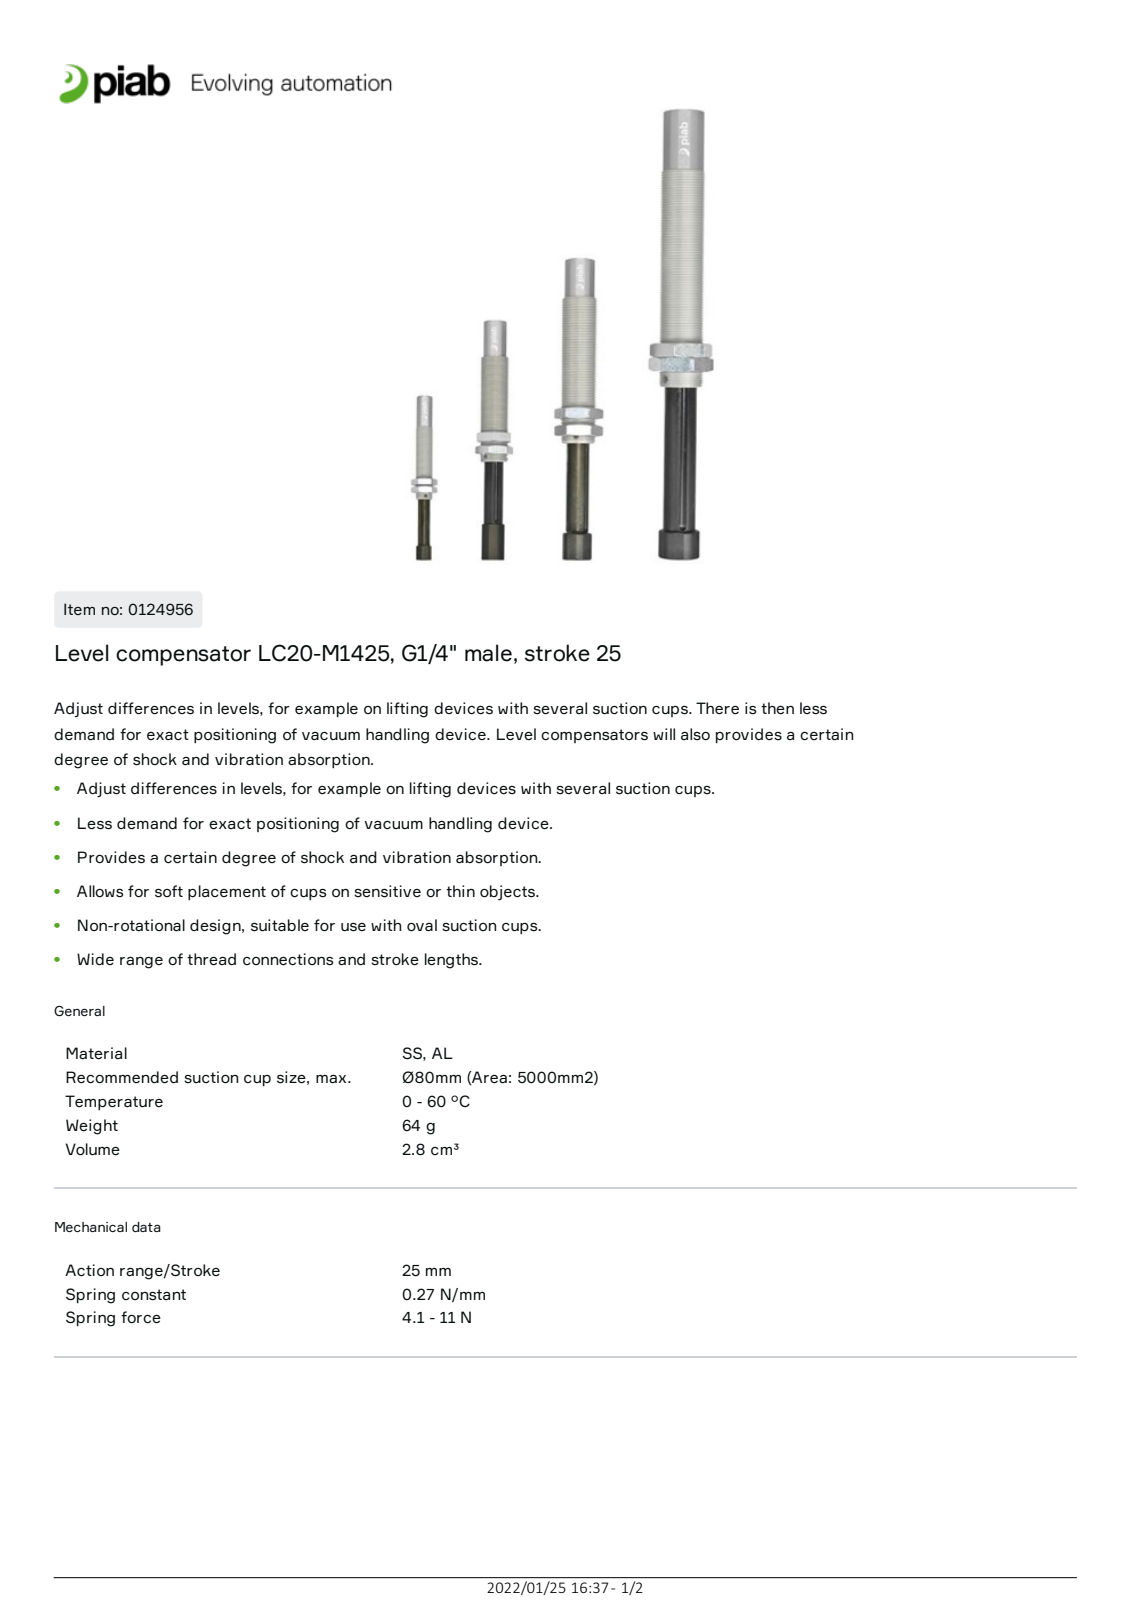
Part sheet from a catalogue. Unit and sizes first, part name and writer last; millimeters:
Units: millimetres
Overall size (bounding box): 121.5 × 36.86 × 27.71
Round holes (diameter × count): ⌀6 ×2, ⌀11.8 ×2, ⌀18.5 ×2, ⌀9.5 ×1, ⌀12.7 ×1
Round bosses / shafts (diameter × count): ⌀20 ×1, ⌀12.5 ×1
Partial cylindrical surfaces — rounded edges, fillets, slot ends (radius × count): R8.4 ×2
Main face-to-face distances: 16, 20, 4, 8, 24, 6, 11, 23, 50, 12
Volume: 44 801 mm³ · Surface area: 30 797 mm²
Bodies: 9 solids, 151 faces (70 planar, 45 cylindrical, 36 other)
Part name (STEP PRODUCT): Body threaded; Nut M20x1.5; Rod vacuum; Piab adaptor nut
STEP written by: Unknown (automotive_design)
